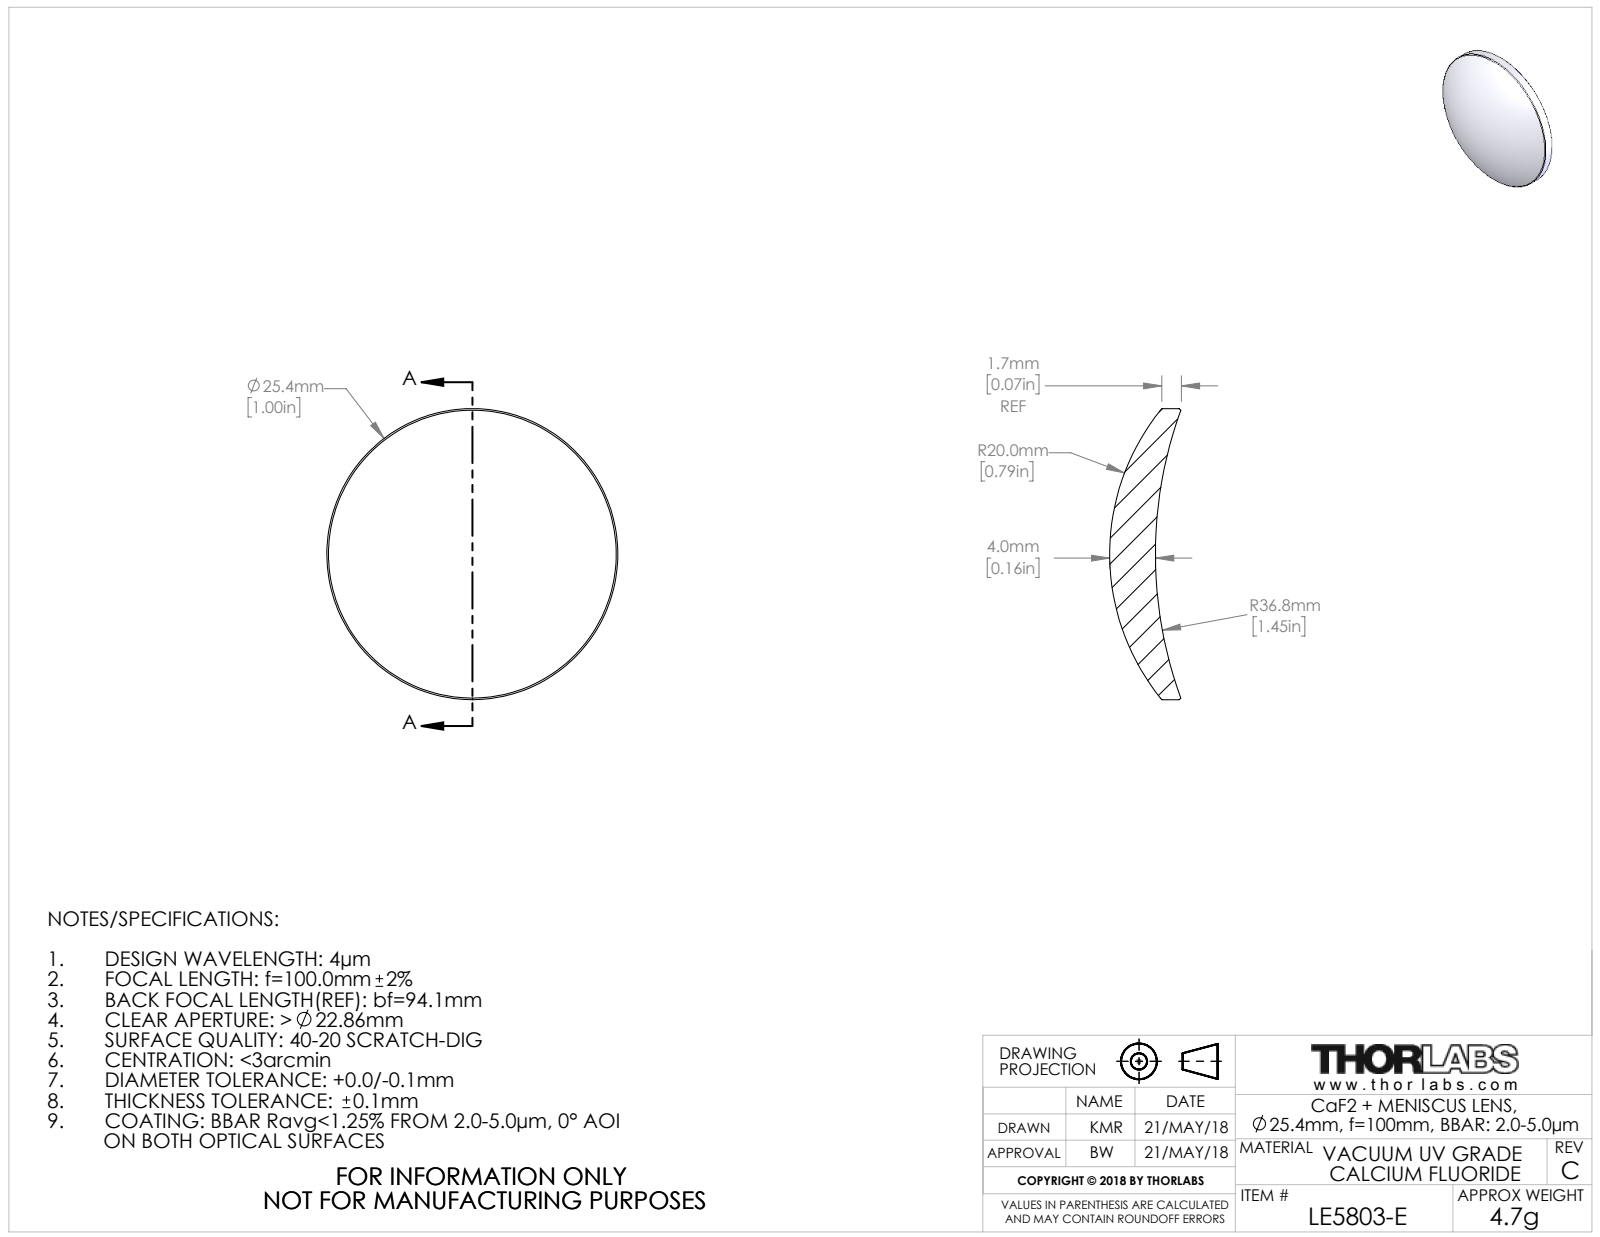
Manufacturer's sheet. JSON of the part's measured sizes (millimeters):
{"part_name": "20163-E0W", "step_written_by": "SolidWorks 2016 (CONFIG_CONTROL_DESIGN)", "units": "millimeters", "bodies": {"solids": 1, "faces": 10, "planar": 0, "cylindrical": 2, "other": 8}, "overall_size": [25.4, 25.4, 6.2], "volume_mm3": 1500, "surface_area_mm2": 1219, "round_bosses_or_shafts": [[25.4, 1]]}
